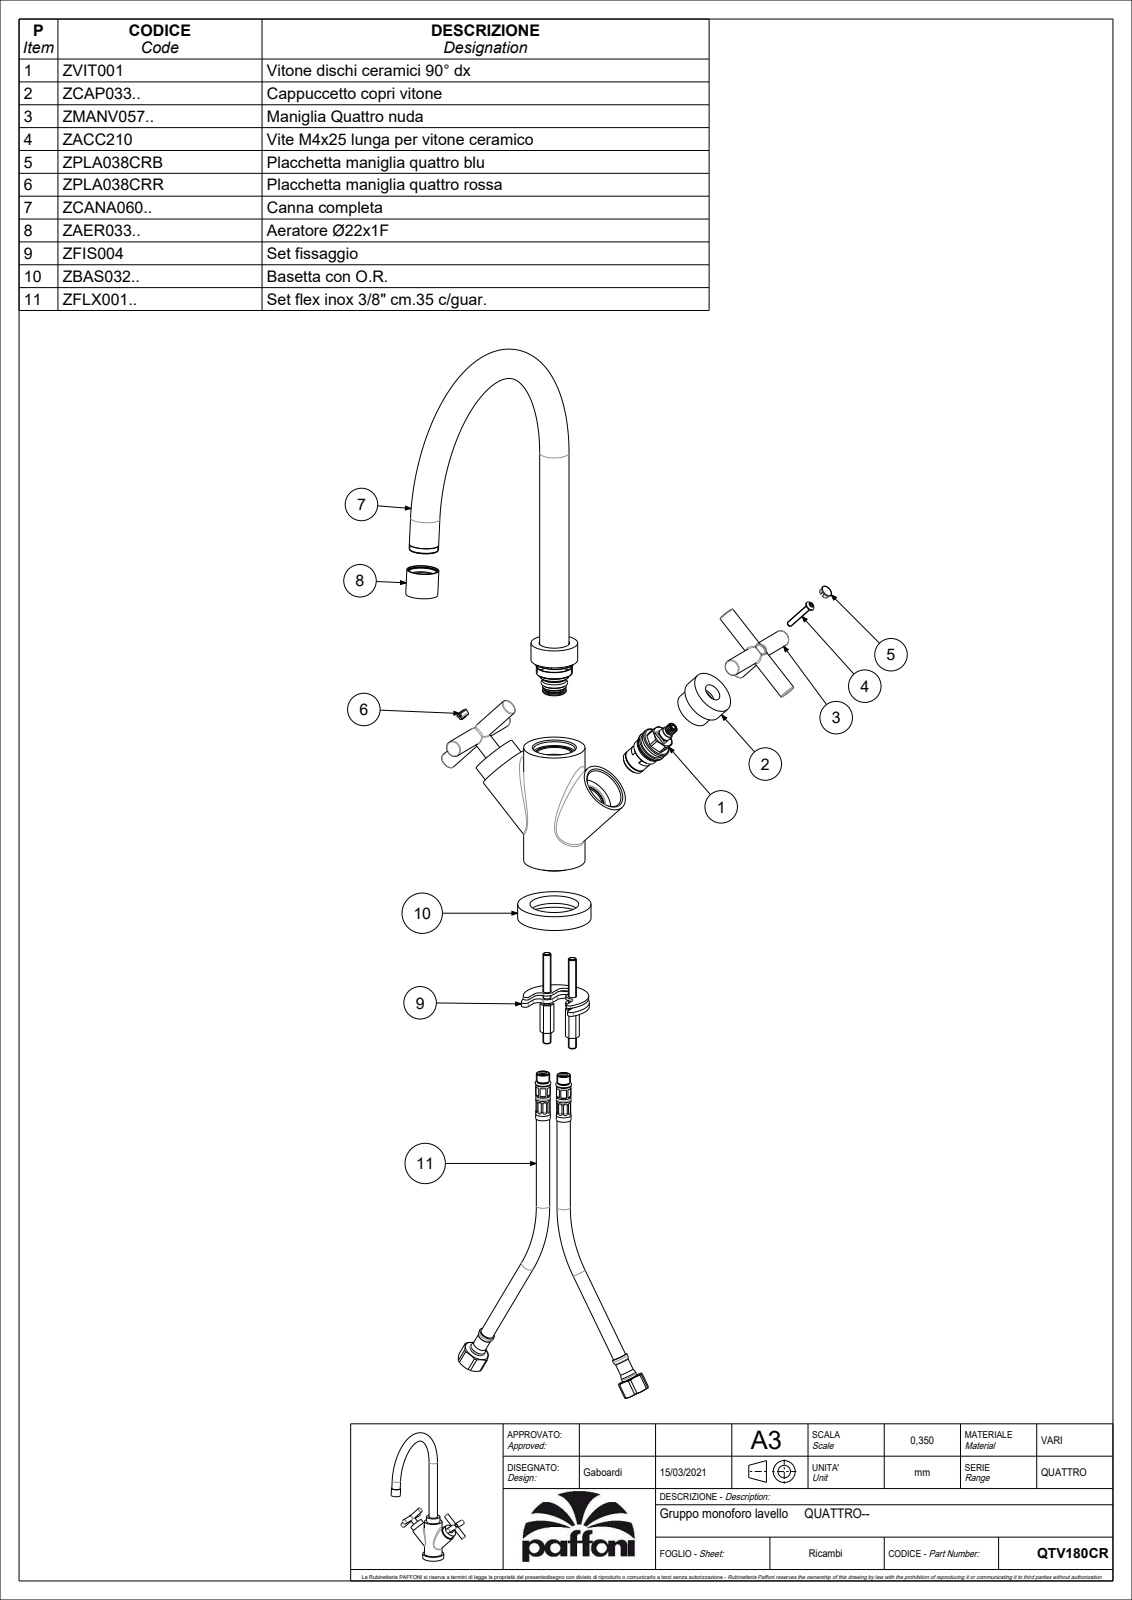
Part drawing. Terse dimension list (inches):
name: QTV180CR
written by: CREO PARAMETRIC BY PTC INC, 2020044 (CONFIG_CONTROL_DESIGN)
unit: in
bodies: 4 solids, 2318 faces (1806 planar, 286 cylindrical, 226 other)
size: 14.732 × 9.704 × 7.583
volume: 18.41 in³; area: 223.3 in²
holes: 6× ⌀0.354, 3× ⌀0.748, 2× ⌀0.13, 2× ⌀0.177, 2× ⌀0.197, 2× ⌀0.276, 2× ⌀0.315, 2× ⌀0.346, 2× ⌀0.374, 2× ⌀0.406, 2× ⌀0.433, 2× ⌀0.531
bosses: 4× ⌀0.472, 3× ⌀0.945, 2× ⌀1.535, 2× ⌀1.339, 2× ⌀1.102, 2× ⌀0.866, 2× ⌀0.843, 2× ⌀0.732
rounds: 34× R0.004, 4× R0.02, 4× R0.039, 2× R0.118, 2× R0.366, 2× R0.37
face distances: 0.157, 0.531, 0.472, 0.039, 0.079, 0.197, 0.059, 3.622, 0.236, 0.02
hole spacings: 0.335, 0.492, 0.535, 0.868, 0.591, 0.866
